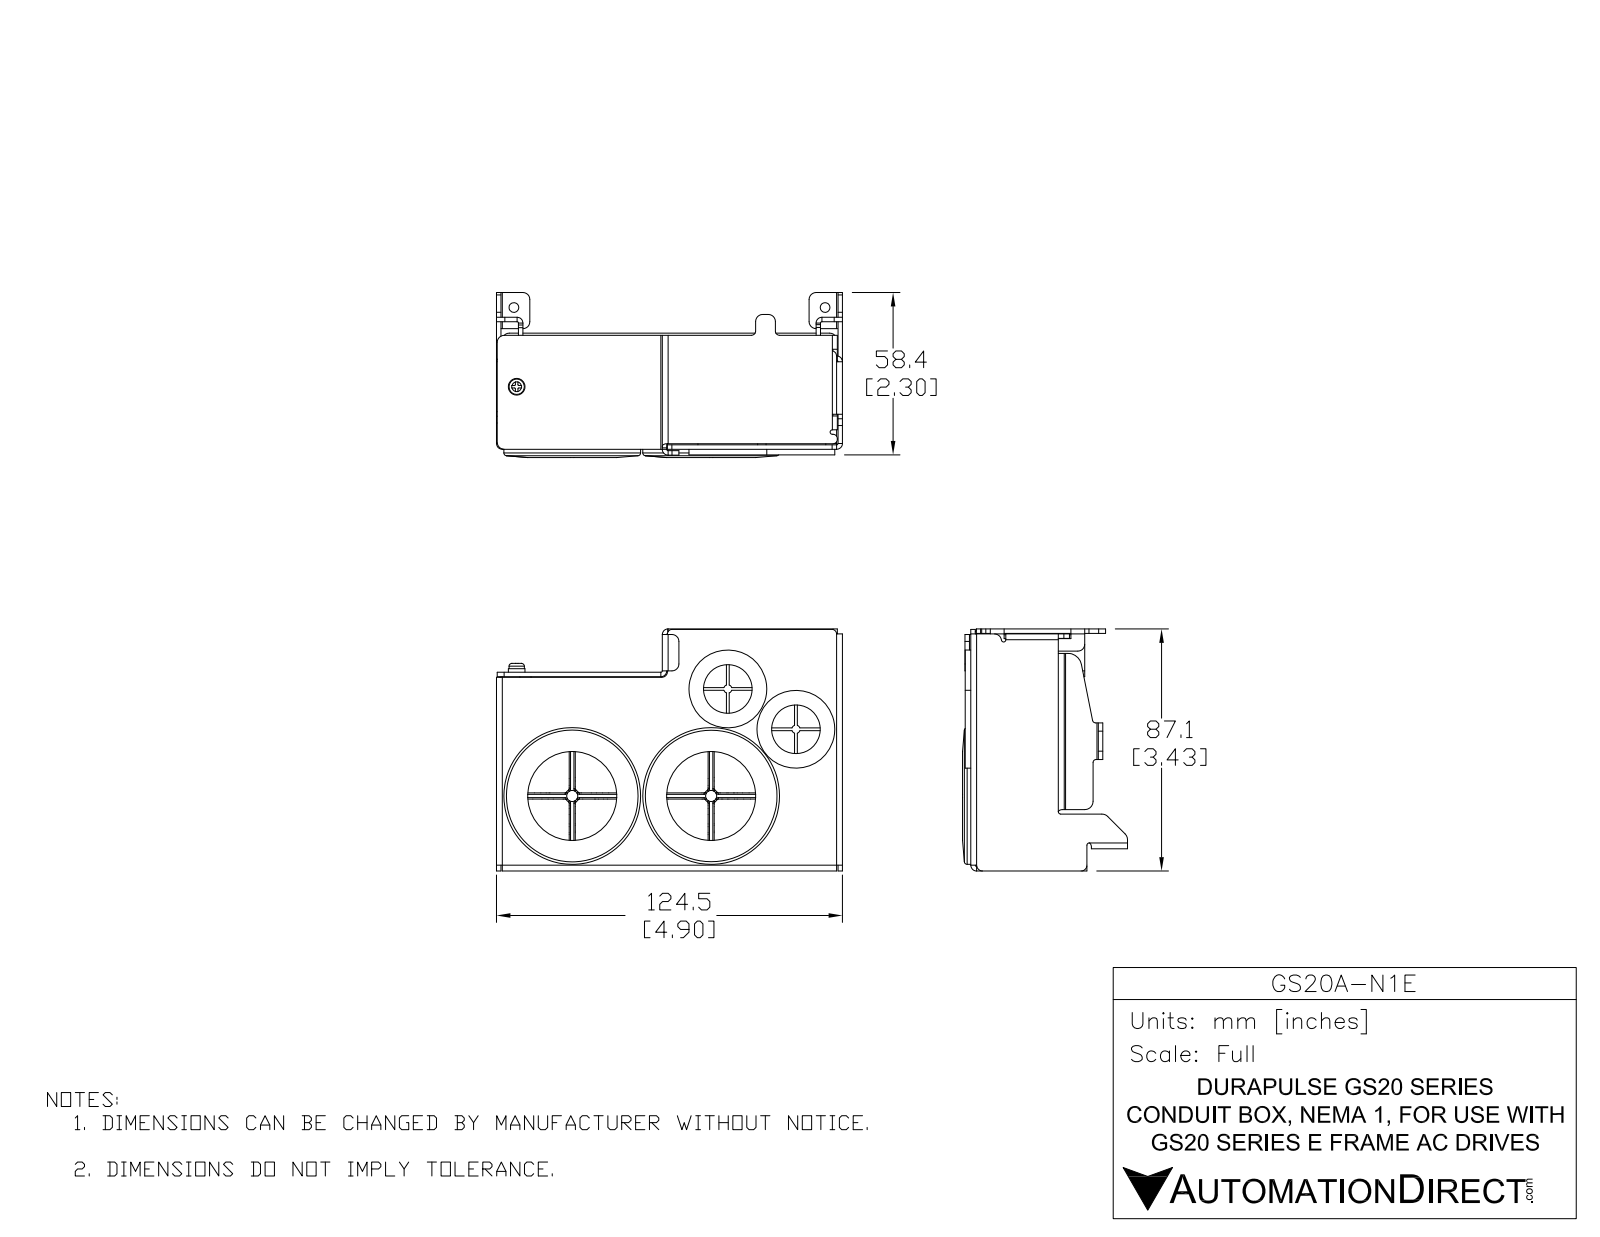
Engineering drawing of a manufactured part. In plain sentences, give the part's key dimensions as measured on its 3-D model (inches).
The part is named "GS20A-N1E". Its 3-D file was written by "SolidWorks 2017 (AUTOMOTIVE_DESIGN)". It is 8 solids with 1188 faces: 416 planar, 211 cylindrical and 561 other. Overall it measures 4.902 by 3.429 by 2.337 inches. Its volume is 3.427 cubic inches and its surface area 107.9 square inches. Round holes: 3 of diameter 0.157, 2 of diameter 0.138, 2 of diameter 0.689, 2 of diameter 0.886, 2 of diameter 1.26, 2 of diameter 1.528, 2 of diameter 1.72, 1 of diameter 0.097, 1 of diameter 0.118. Round bosses or shafts: 2 of diameter 1.937, 2 of diameter 1.724, 2 of diameter 1.102, 2 of diameter 0.846, 1 of diameter 0.236, 1 of diameter 0.22, 1 of diameter 0.217, 1 of diameter 0.193. Partial cylindrical surfaces (rounded edges, fillets, slot ends): 19 of radius 0.039, 18 of radius 0.083, 16 of radius 0.02, 16 of radius 0.098, 7 of radius 0.118, 6 of radius 0.031, 6 of radius 0.059, 4 of radius 0.012. The main face-to-face distances are 0.063, 2.752, 0.614, 3.366, 4.839, 2.689, 0.677, 0.551, 2.815, 3.429. The hole center spacings are 1.121, 1.123, 1.528, 1.534, 1.969, 2.676, 3.307, 4.409.
